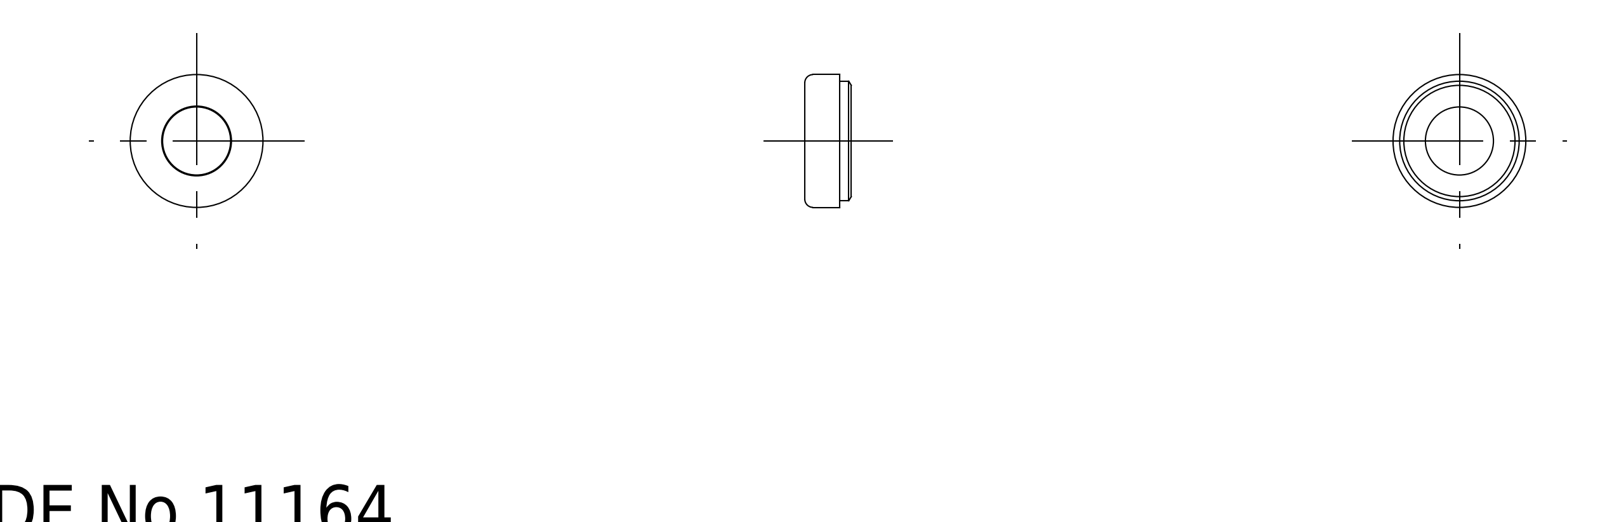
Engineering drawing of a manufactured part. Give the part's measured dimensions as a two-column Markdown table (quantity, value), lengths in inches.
| quantity | value |
| --- | --- |
| part name | washer; packing; TL_421_M4 |
| STEP written by | SolidWorks 2015 (AUTOMOTIVE_DESIGN) |
| units | inches |
| bodies | 2 solids, 22 faces (6 planar, 12 cylindrical, 4 other) |
| overall size | 0.315 × 0.315 × 0.11 |
| volume | 0.006 in³ |
| surface area | 0.457 in² |
| round holes (diameter × count) | 0.161 × 1, 0.165 × 1, 0.276 × 1 |
| round bosses / shafts (diameter × count) | 0.315 × 1, 0.283 × 1 |
| main face-to-face distances | 0.02, 0.11, 0.091, 0.083, 0.063, 0.028 |
